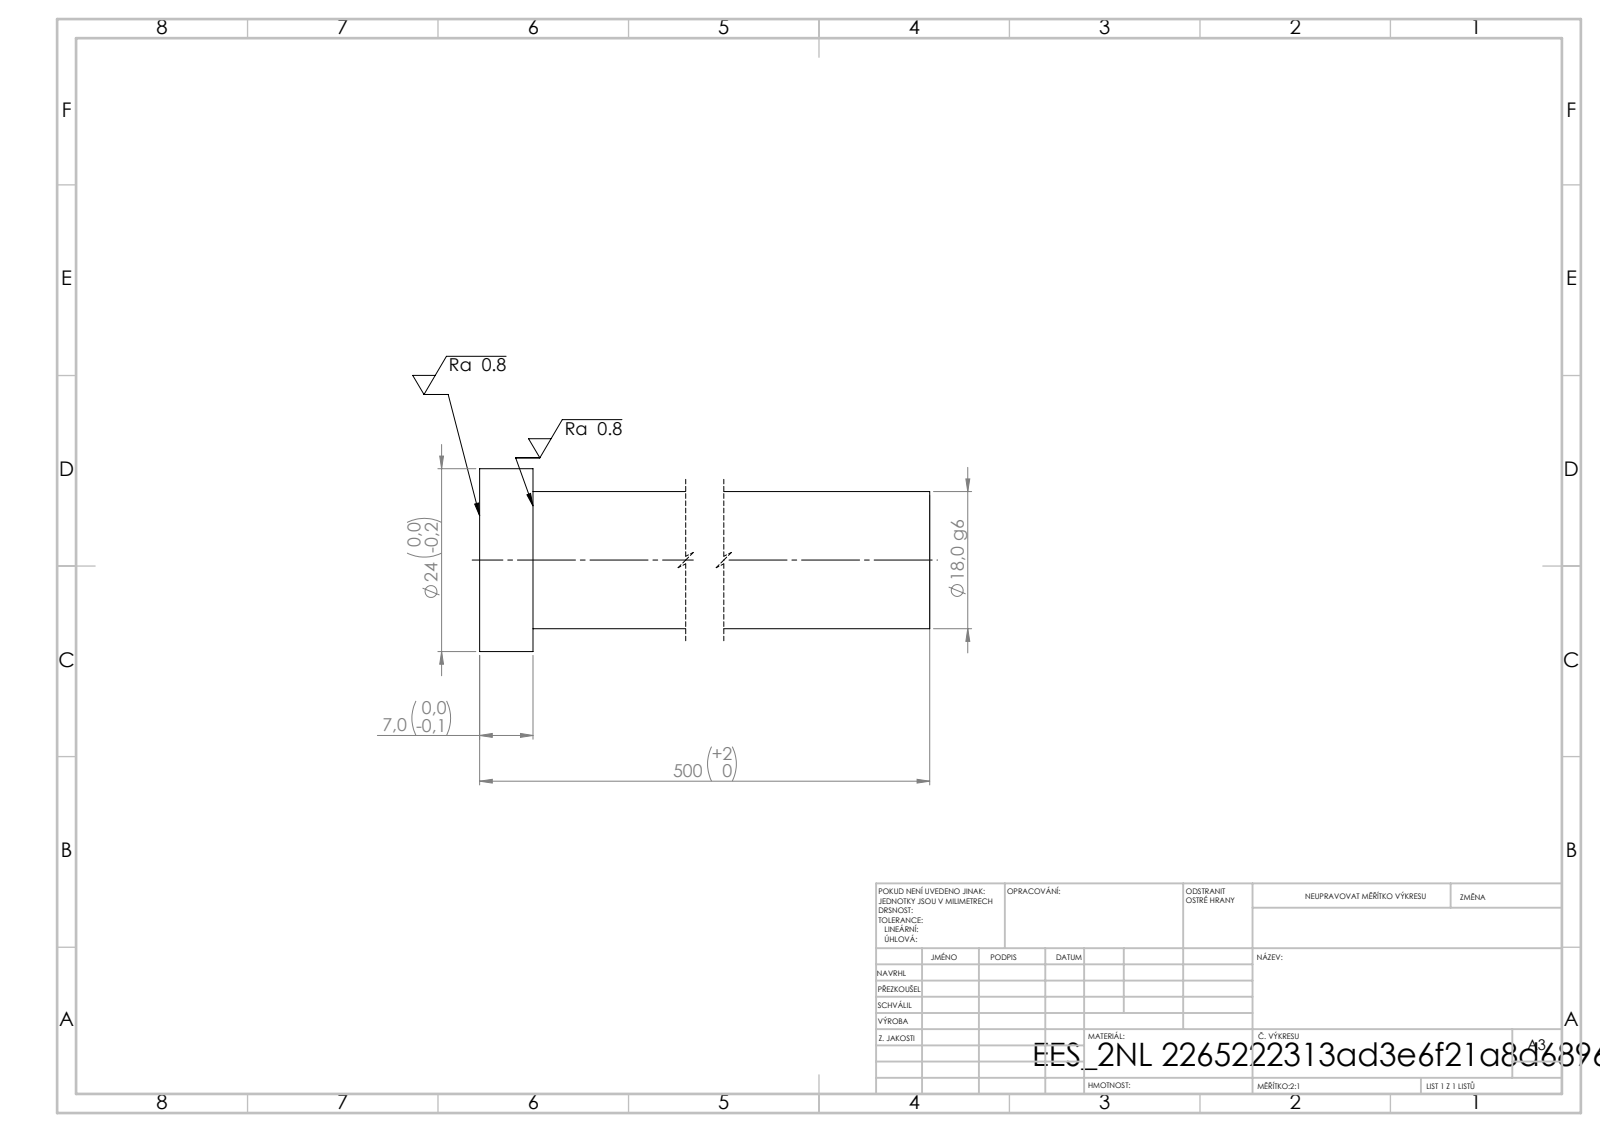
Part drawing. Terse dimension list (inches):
written by: SolidWorks 2019 (CONFIG_CONTROL_DESIGN)
unit: in
bodies: 1 solid, 7 faces (3 planar, 4 cylindrical, 0 other)
size: 19.685 × 0.945 × 0.945
volume: 7.849 in³; area: 45.43 in²
bosses: 1× ⌀0.945, 1× ⌀0.709
face distances: 19.685, 0.276, 19.409
